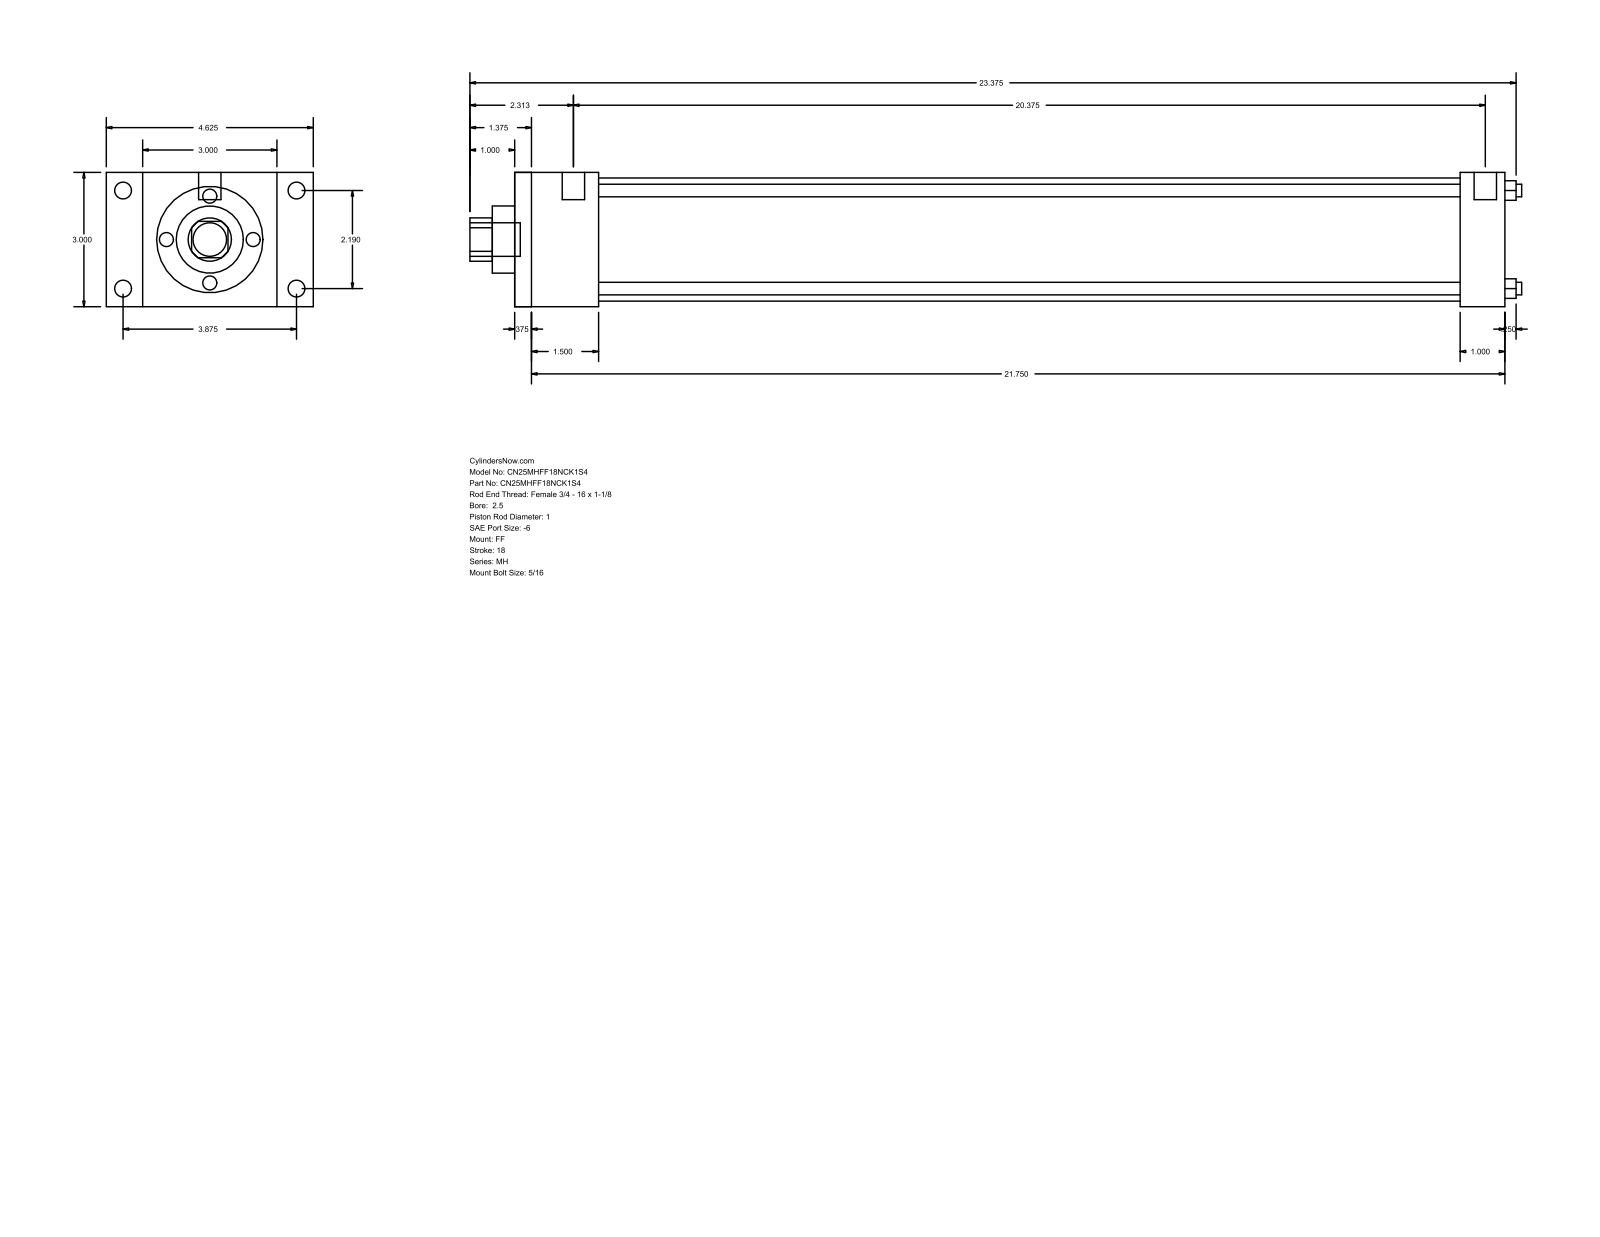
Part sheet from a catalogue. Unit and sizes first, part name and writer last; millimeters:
Units: millimetres
Overall size (bounding box): 596.9 × 117.47 × 76.2
Round holes (diameter × count): ⌀7.14 ×4, ⌀25.4 ×1, ⌀38.1 ×1, ⌀69.85 ×1
Round bosses / shafts (diameter × count): ⌀9.53 ×4, ⌀5.56 ×4, ⌀12.7 ×2, ⌀19.05 ×1
Partial cylindrical surfaces — rounded edges, fillets, slot ends (radius × count): R12.29 ×1
Main face-to-face distances: 76.2, 561.98, 9.52, 552.46, 25.4, 47.63, 536.58, 38.11, 527.06, 488.95
Hole centre spacings: 39.33, 55.62, 78.66
Bodies: 0 solids, 92 faces (64 planar, 28 cylindrical, 0 other)
Part name (STEP PRODUCT): MH_FF__0250_1
STEP written by: GSSL Pune (CONFIG_CONTROL_DESIGN)
